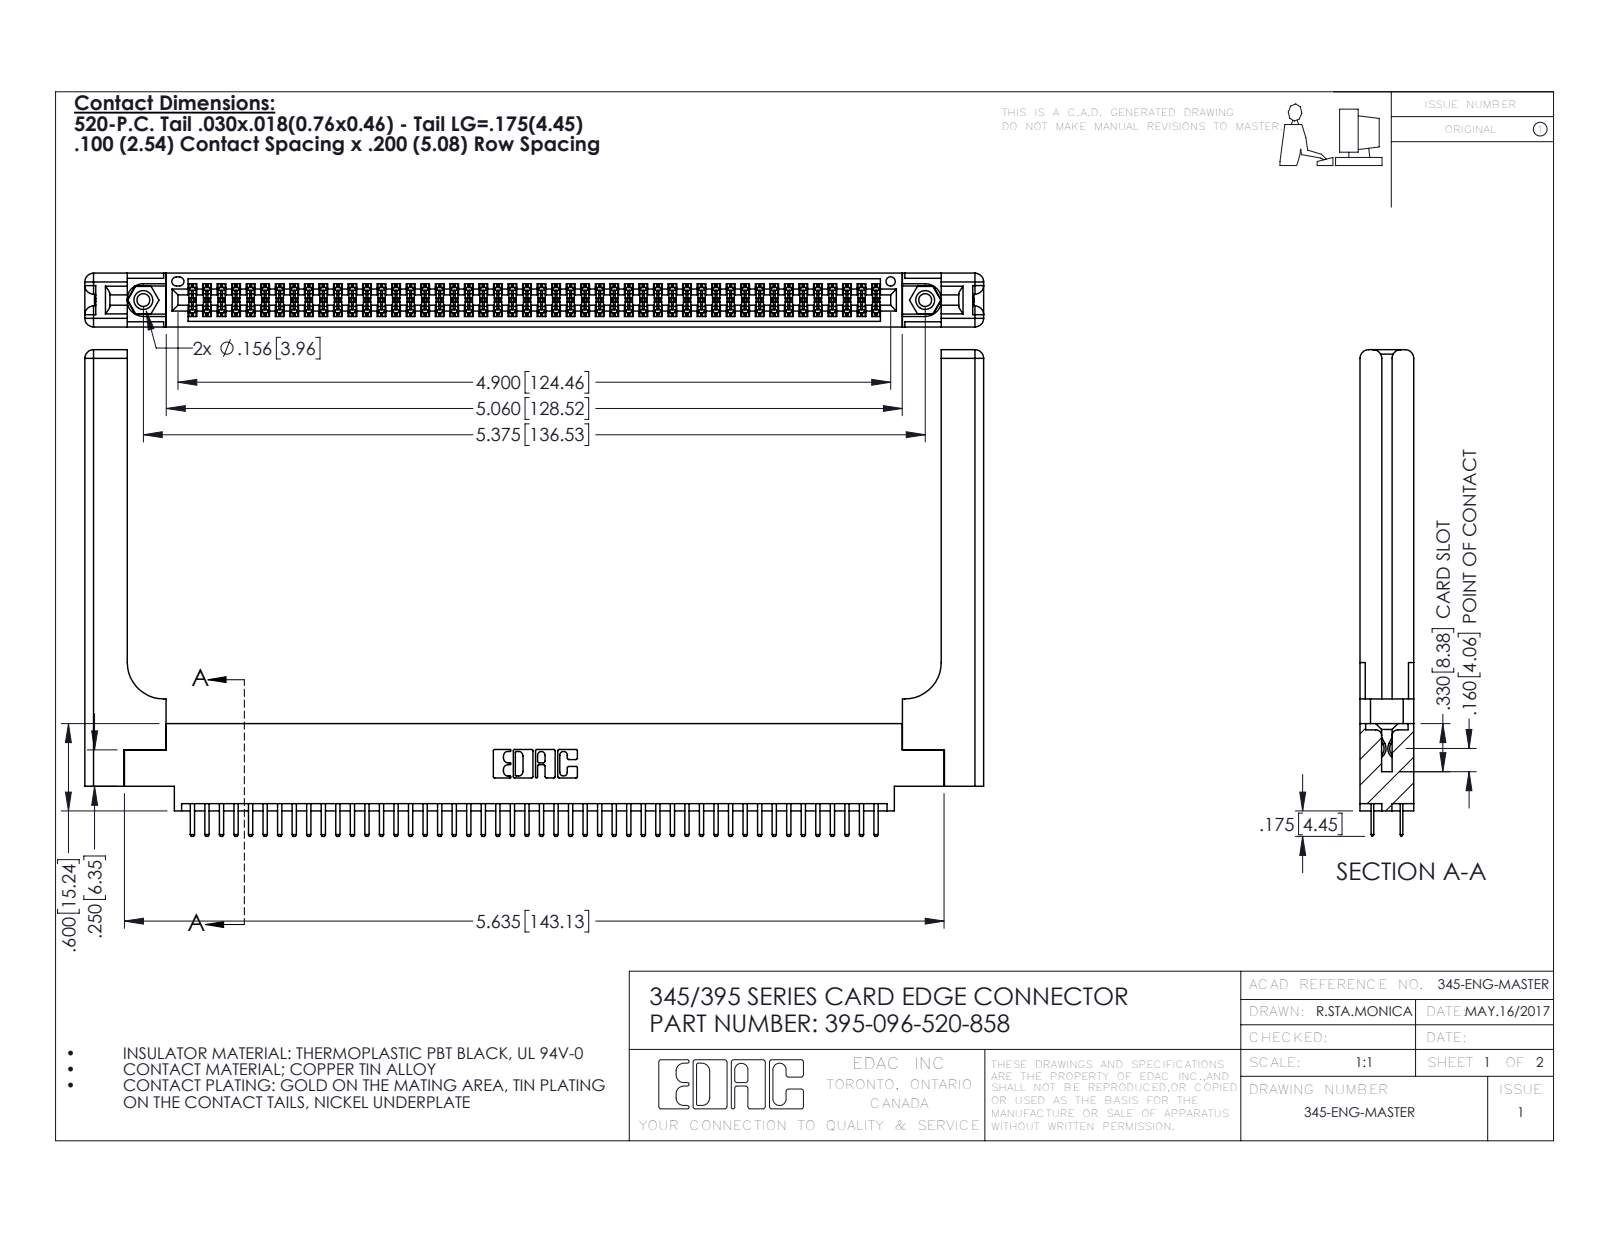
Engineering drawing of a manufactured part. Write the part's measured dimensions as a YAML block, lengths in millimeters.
part_name: "345 Part_0.170 Offset - 0.156 Dia-TH; 345-250-001_345-250-001-102; 395-096-520-858; 345-220-058_345-220-058 (+1 more)"
step_written_by: "SolidWorks 2016 (CONFIG_CONTROL_DESIGN)"
units: millimeters
bodies: {solids: 101, faces: 5570, planar: 3592, cylindrical: 1918, other: 60}
overall_size: [156.9, 85, 9.4]
volume: 23610
surface_area: 27620
round_holes:
  - {diameter: 2.3, count: 2}
  - {diameter: 3.2, count: 2}
  - {diameter: 4, count: 2}
  - {diameter: 1.6, count: 1}
round_bosses_or_shafts:
  - {diameter: 3.9, count: 2}
partial_cylinders:
  - {radius: 0.2, count: 145}
  - {radius: 0.3, count: 100}
  - {radius: 0.3, count: 22}
  - {radius: 1.5, count: 16}
  - {radius: 0.2, count: 6}
  - {radius: 0.8, count: 6}
  - {radius: 0.7, count: 3}
  - {radius: 0.4, count: 2}
face_to_face_distances: [9.4, 1.8, 7.6, 5.1, 2.5, 6.9, 0.6, 5.7, 3.8, 3.8]
hole_center_spacings: [6.9, 130.5, 136.5]
